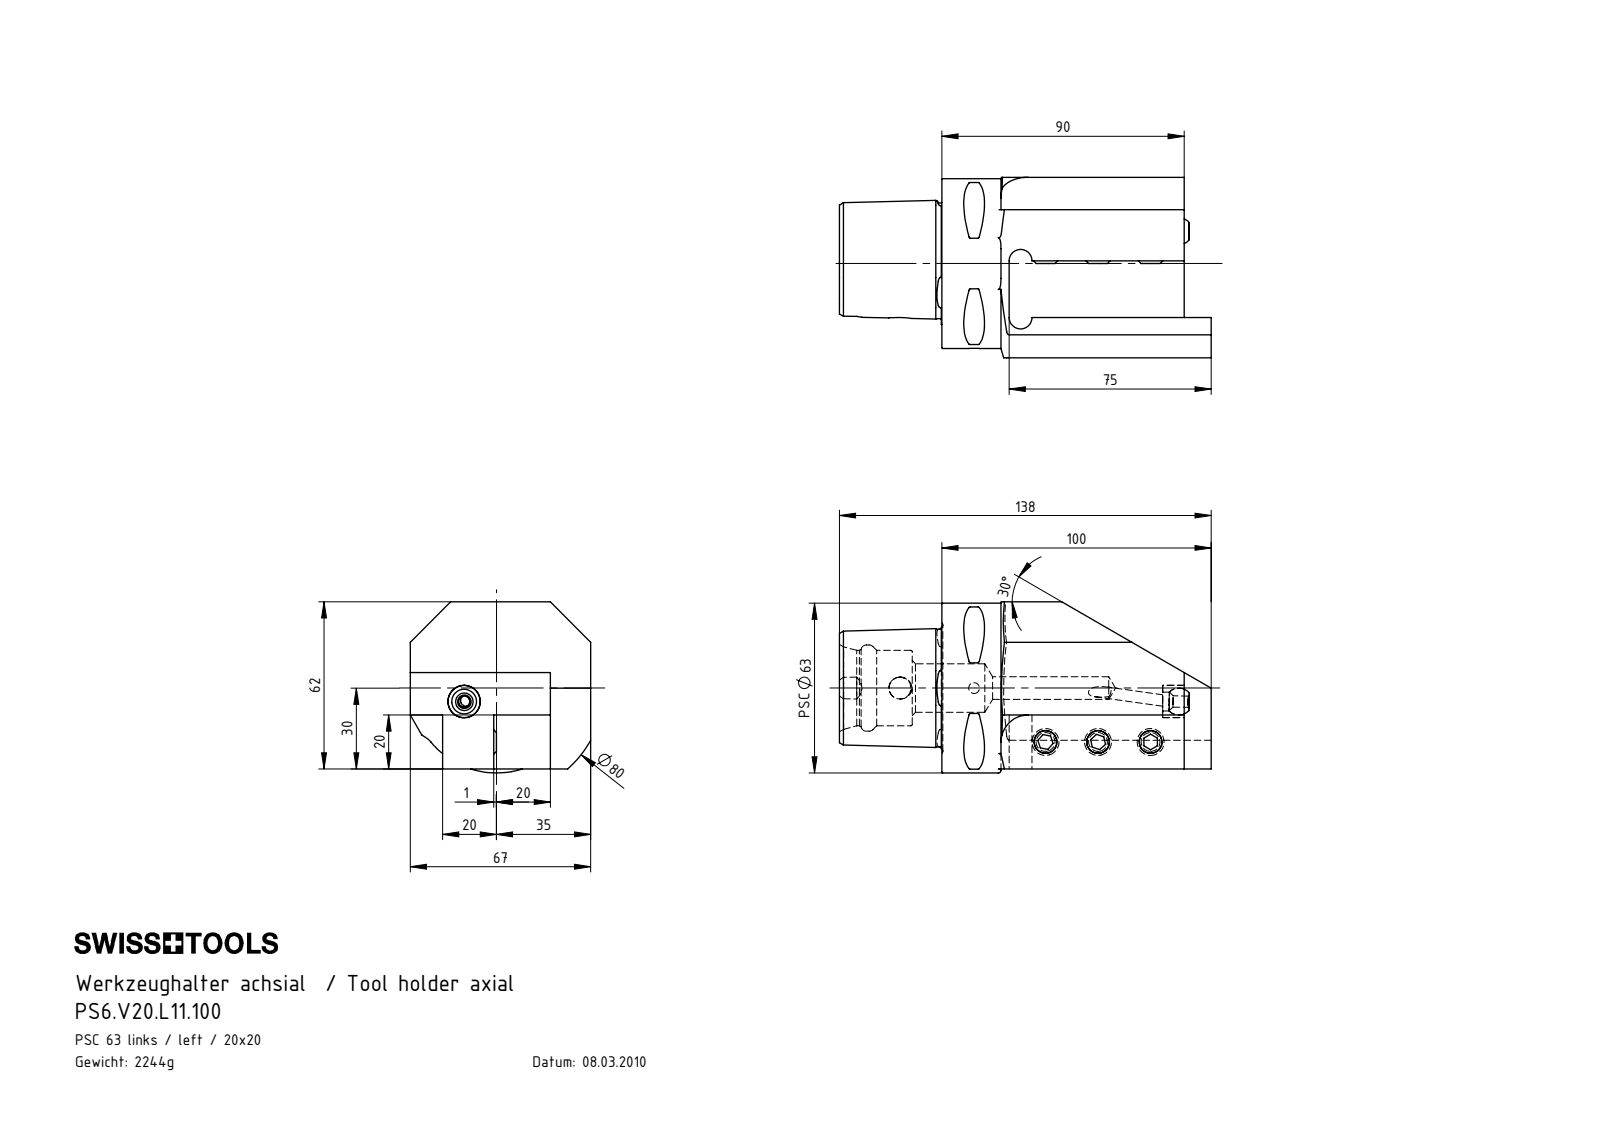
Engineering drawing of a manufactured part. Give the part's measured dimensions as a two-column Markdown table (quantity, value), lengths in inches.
| quantity | value |
| --- | --- |
| part name | PS6.V20.L11.100; KU1-U12.001.010_1; ISO 4026 - M10 x 20; KU1-U12.001.010 (+2 more) |
| STEP written by | SolidWorks 2017 (AUTOMOTIVE_DESIGN) |
| units | inches |
| bodies | 6 solids, 218 faces (67 planar, 53 cylindrical, 98 other) |
| overall size | 5.433 × 2.638 × 2.5 |
| volume | 17.42 in³ |
| surface area | 70.41 in² |
| round holes (diameter × count) | 0.335 × 3, 0.165 × 2, 0.157 × 1, 0.276 × 1, 0.319 × 1, 0.331 × 1, 0.472 × 1, 0.709 × 1, 1.102 × 1, 1.26 × 1 |
| round bosses / shafts (diameter × count) | 0.394 × 3, 2.48 × 1 |
| partial cylindrical surfaces (radius × count) | 0.02 × 8, 0.205 × 2, 0.236 × 1, 0.394 × 1, 1.575 × 1 |
| main face-to-face distances | 0.787, 2.638, 0.591, 2.047, 2.165, 1.575, 0.472, 1.417, 3.543, 0.827 |
| hole center spacings | 0.768, 0.512, 1.083, 1.307, 1.535, 1.975, 2.267, 2.696 |
